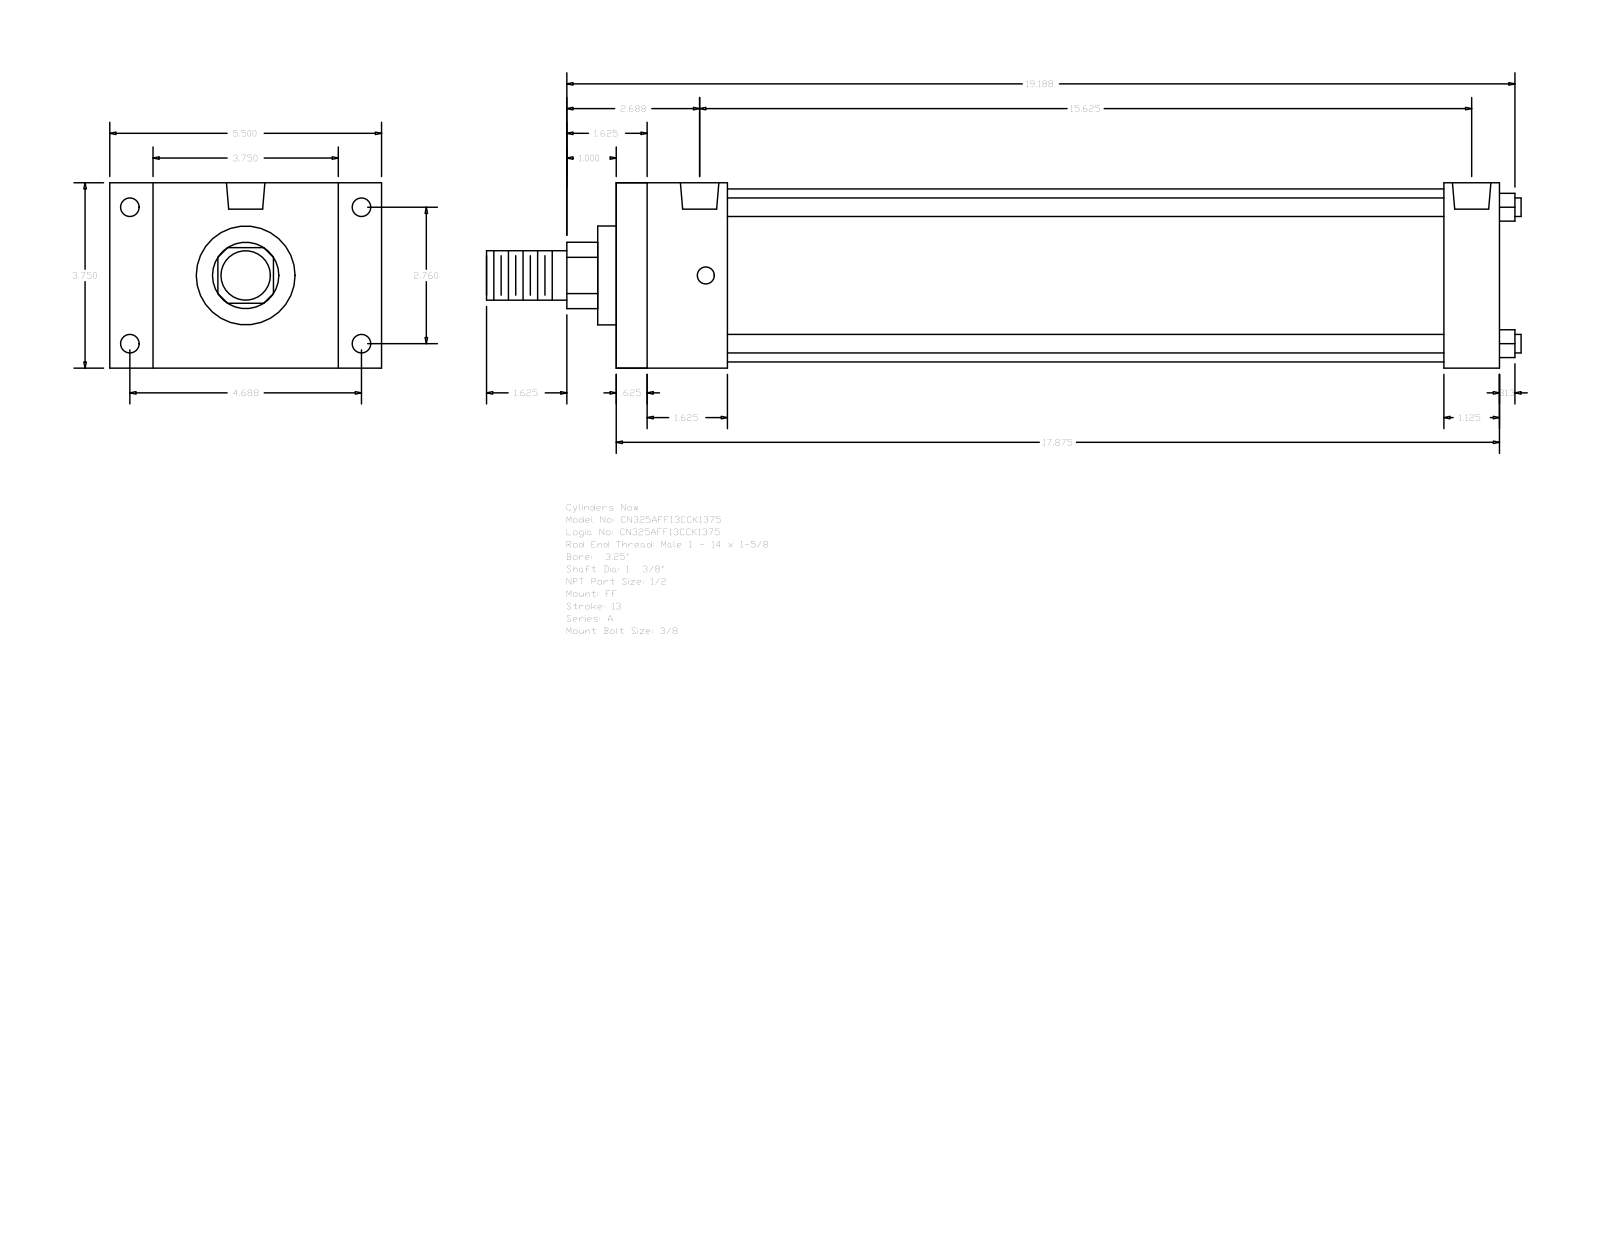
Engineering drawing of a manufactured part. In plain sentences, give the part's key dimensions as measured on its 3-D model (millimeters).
The part is named "A_FF__0325_1.375". Its 3-D file was written by "GSSL Pune (CONFIG_CONTROL_DESIGN)". It is 0 solids with 92 faces: 64 planar, 28 cylindrical and 0 other. Overall it measures 531.81 by 139.7 by 95.25 millimeters. Round holes: 4 of diameter 8.73, 4 of diameter 9.53, 2 of diameter 19.77. Round bosses or shafts: 4 of diameter 9.53, 1 of diameter 88.9, 1 of diameter 50.8, 1 of diameter 34.92, 1 of diameter 25.4. Partial cylindrical surfaces (rounded edges, fillets, slot ends): 1 of radius 17.06. The main face-to-face distances are 95.24, 454.03, 15.87, 438.16, 57.15, 28.58, 22.23, 117.47, 425.45, 41.28. The hole center spacings are 3.18, 70.1, 119.06, 138.16, 390.52, 393.7, 396.88.
